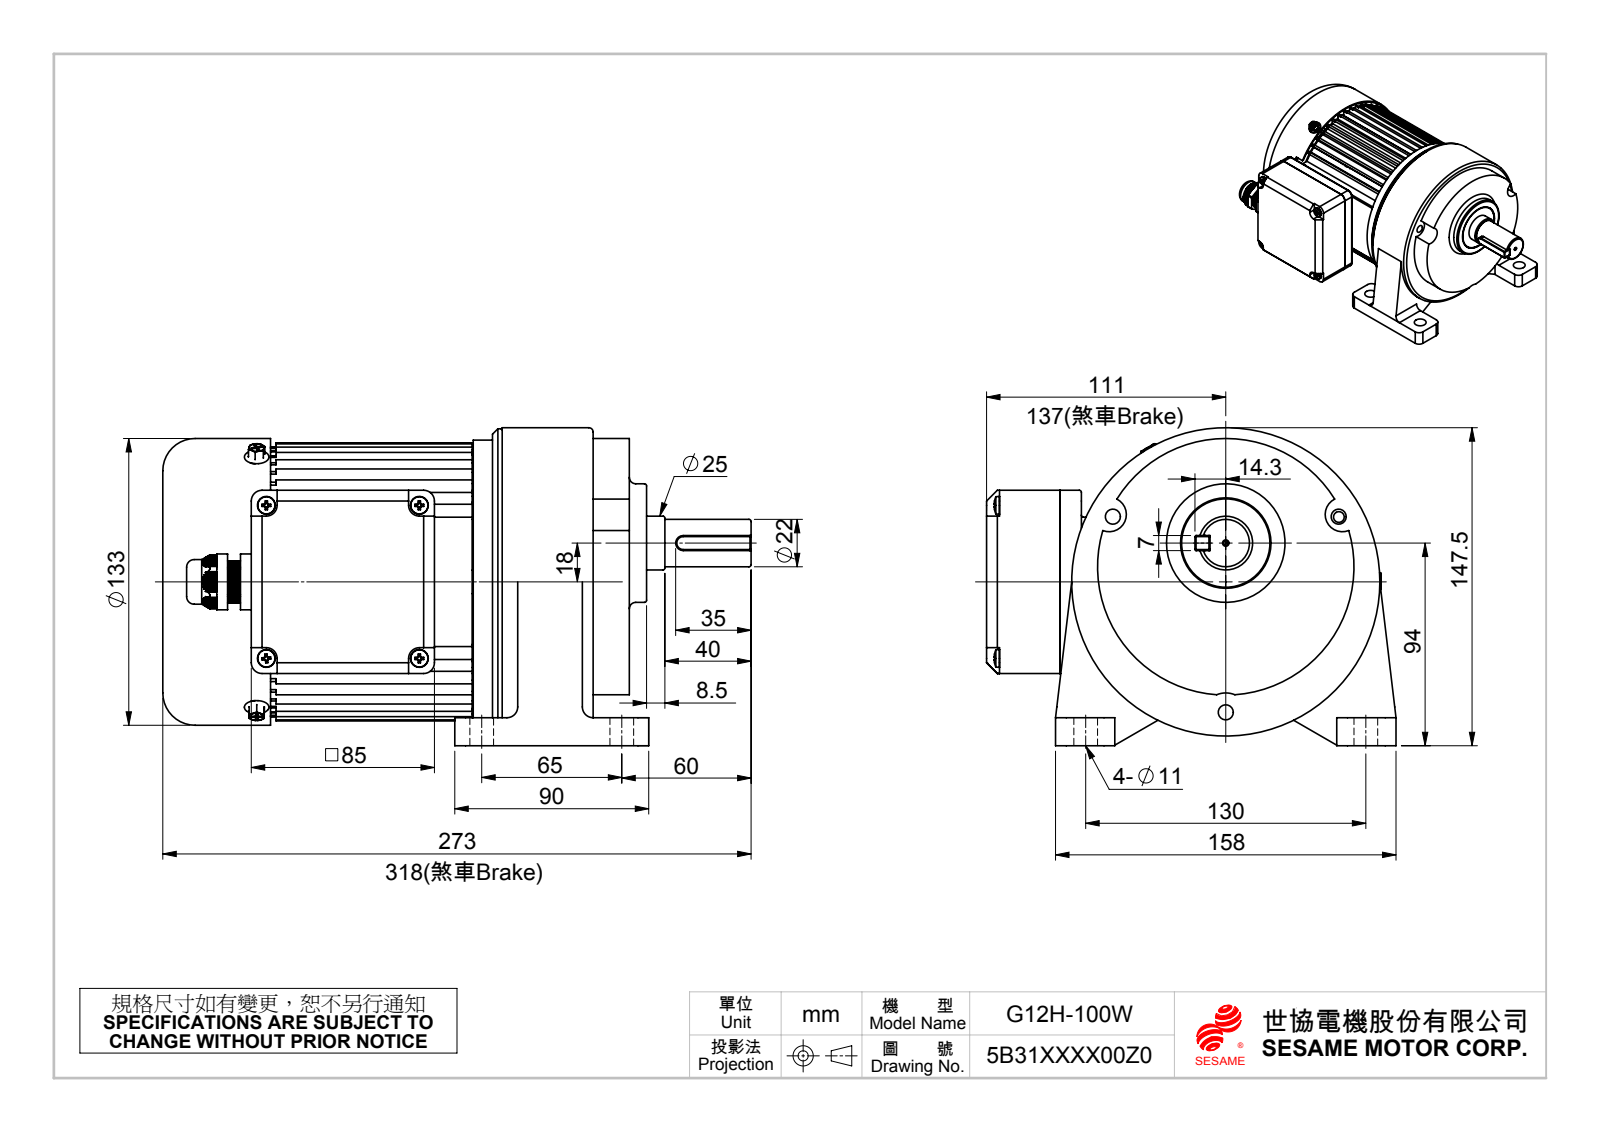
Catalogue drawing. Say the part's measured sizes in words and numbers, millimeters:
The part is named "出線盒下蓋; 出線盒上蓋; G12OS1-02; G12-200 (+8 more)". Its 3-D file was written by "SolidWorks 2010 (CONFIG_CONTROL_DESIGN)". It is 19 solids with 2640 faces: 794 planar, 837 cylindrical and 1009 other. Overall it measures 273 by 190 by 147.5 millimeters. Its volume is 2 970 000 cubic millimeters and its surface area 399 328 square millimeters. Round holes: 14 of diameter 5, 9 of diameter 3.3, 4 of diameter 8, 4 of diameter 11, 3 of diameter 4.2, 3 of diameter 7, 1 of diameter 2, 1 of diameter 7.5, 1 of diameter 10.8, 1 of diameter 16.5, 1 of diameter 24.95, 1 of diameter 42. Round bosses or shafts: 4 of diameter 8.3, 4 of diameter 4, 3 of diameter 5, 1 of diameter 143, 1 of diameter 142, 1 of diameter 133, 1 of diameter 131.5, 1 of diameter 131. Partial cylindrical surfaces (rounded edges, fillets, slot ends): 74 of radius 1, 18 of radius 5, 8 of radius 1.03, 6 of radius 2.75, 4 of radius 2, 4 of radius 2.55, 4 of radius 3.55, 2 of radius 8. The main face-to-face distances are 2, 10, 18.95, 95, 113.95, 13, 18, 105, 123.95, 3. The hole center spacings are 60.5, 104.79, 45, 71, 31.13, 11, 11.5, 14.66.
